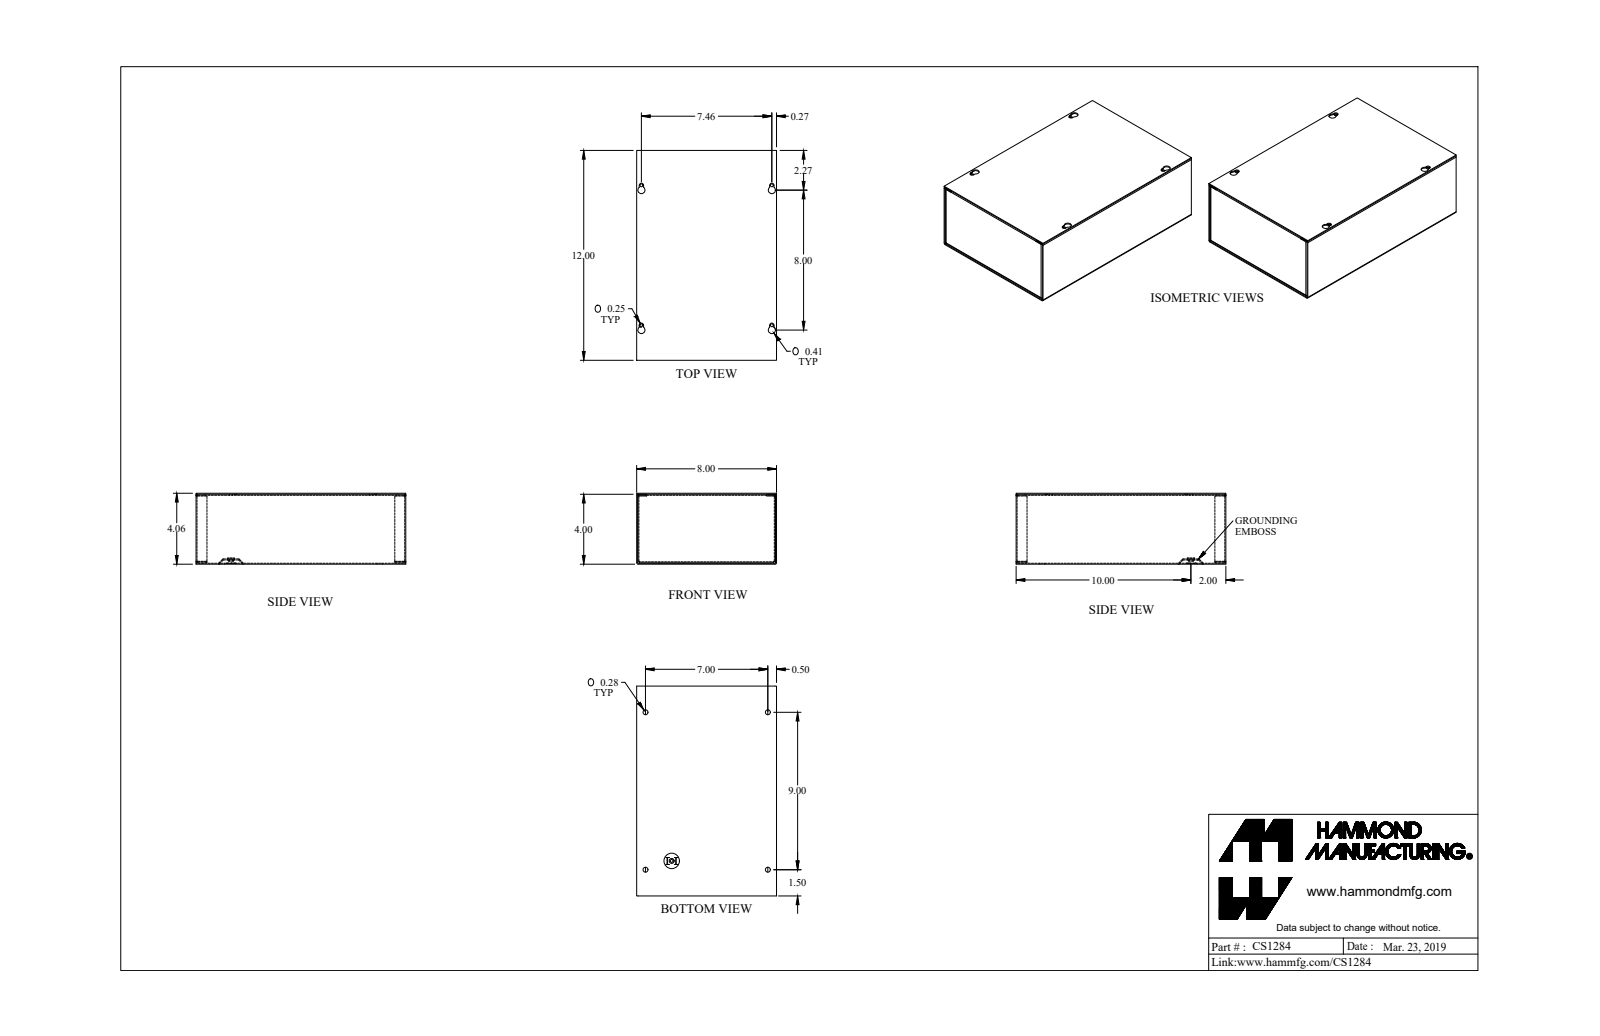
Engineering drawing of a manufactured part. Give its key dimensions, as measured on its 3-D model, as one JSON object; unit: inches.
{"part_name": "CS1284_Default", "step_written_by": "SolidWorks 2019 (CONFIG_CONTROL_DESIGN)", "units": "inches", "bodies": {"solids": 4, "faces": 205, "planar": 125, "cylindrical": 72, "other": 8}, "overall_size": [12, 8, 4.057], "volume_in3": 21.61, "surface_area_in2": 767.7, "round_holes": [[0.17, 5], [0.281, 4], [0.5, 1]], "round_bosses_or_shafts": [[0.492, 1], [0.284, 1]], "partial_cylinders_radius": [[0.029, 12], [0.086, 12], [0.057, 8], [0.125, 4], [0.203, 4]], "face_to_face_distances": [0.057, 4, 3.943, 4.057, 7.943, 11.943, 8, 7.886, 12, 11.886], "hole_center_spacings": [0.55, 7.247, 8.503, 11.159, 7, 7.46, 8, 9]}
